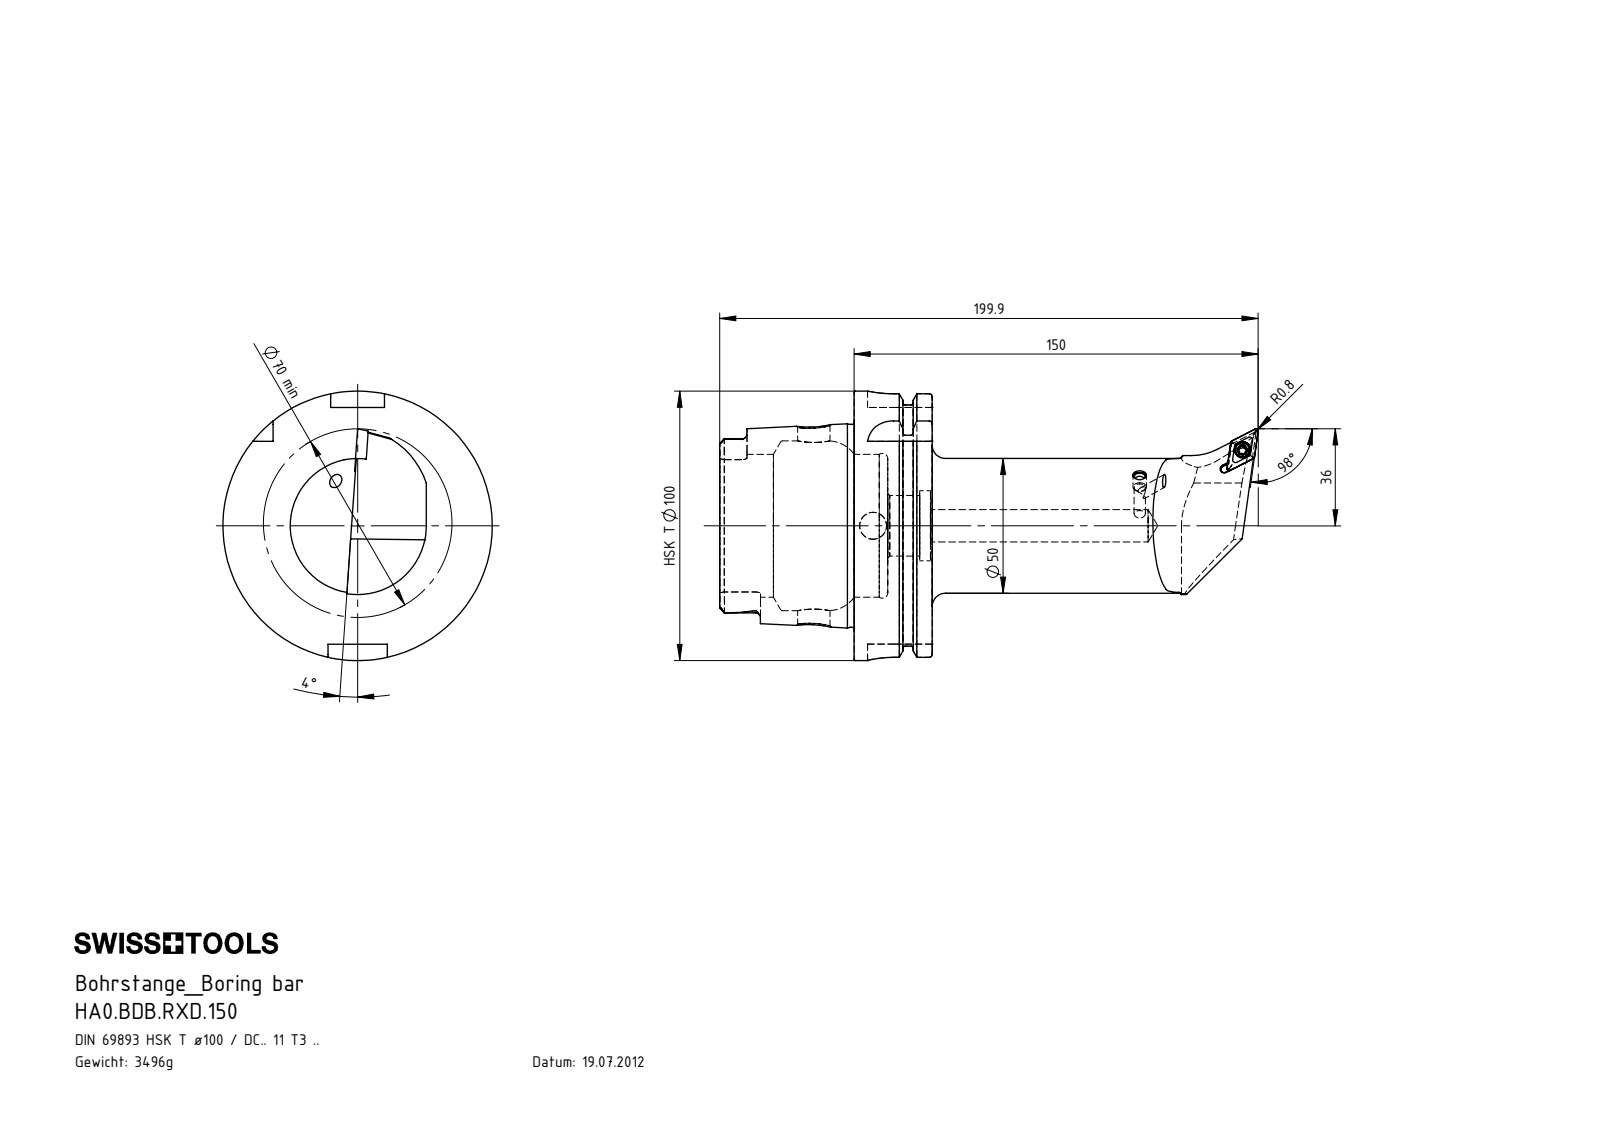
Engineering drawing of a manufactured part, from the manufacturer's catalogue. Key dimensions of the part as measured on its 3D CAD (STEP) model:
Part name (STEP PRODUCT): WCB-ER2.001.009_A; DCMT11T308; HA0-BDB.RXD.150_A; HA0.BDB.RXD.150 (+1 more)
STEP written by: SolidWorks 2017 (CONFIG_CONTROL_DESIGN)
Units: millimetres
Bodies: 5 solids, 315 faces (74 planar, 92 cylindrical, 149 other)
Overall size (bounding box): 199.91 × 100 × 100
Volume: 444 915 mm³ · Surface area: 70 916 mm²
Round holes (diameter × count): ⌀5 ×2, ⌀12 ×2, ⌀3.3 ×1, ⌀4 ×1, ⌀4.4 ×1, ⌀6 ×1, ⌀6.1 ×1, ⌀10 ×1, ⌀22.5 ×1, ⌀26 ×1, ⌀53 ×1, ⌀63 ×1
Round bosses / shafts (diameter × count): ⌀100 ×1, ⌀91.95 ×1, ⌀75.26 ×1, ⌀50 ×1, ⌀5.25 ×1, ⌀5 ×1, ⌀4 ×1
Partial cylindrical surfaces — rounded edges, fillets, slot ends (radius × count): R0.34 ×6, R0.59 ×6, R1.9 ×6, R4.88 ×4, R10 ×4, R1.25 ×1, R6 ×1, R21 ×1
Main face-to-face distances: 28.95, 12.45, 16.5, 49.9, 62.35, 78.85, 87.8, 78.2, 28.3, 15.85
